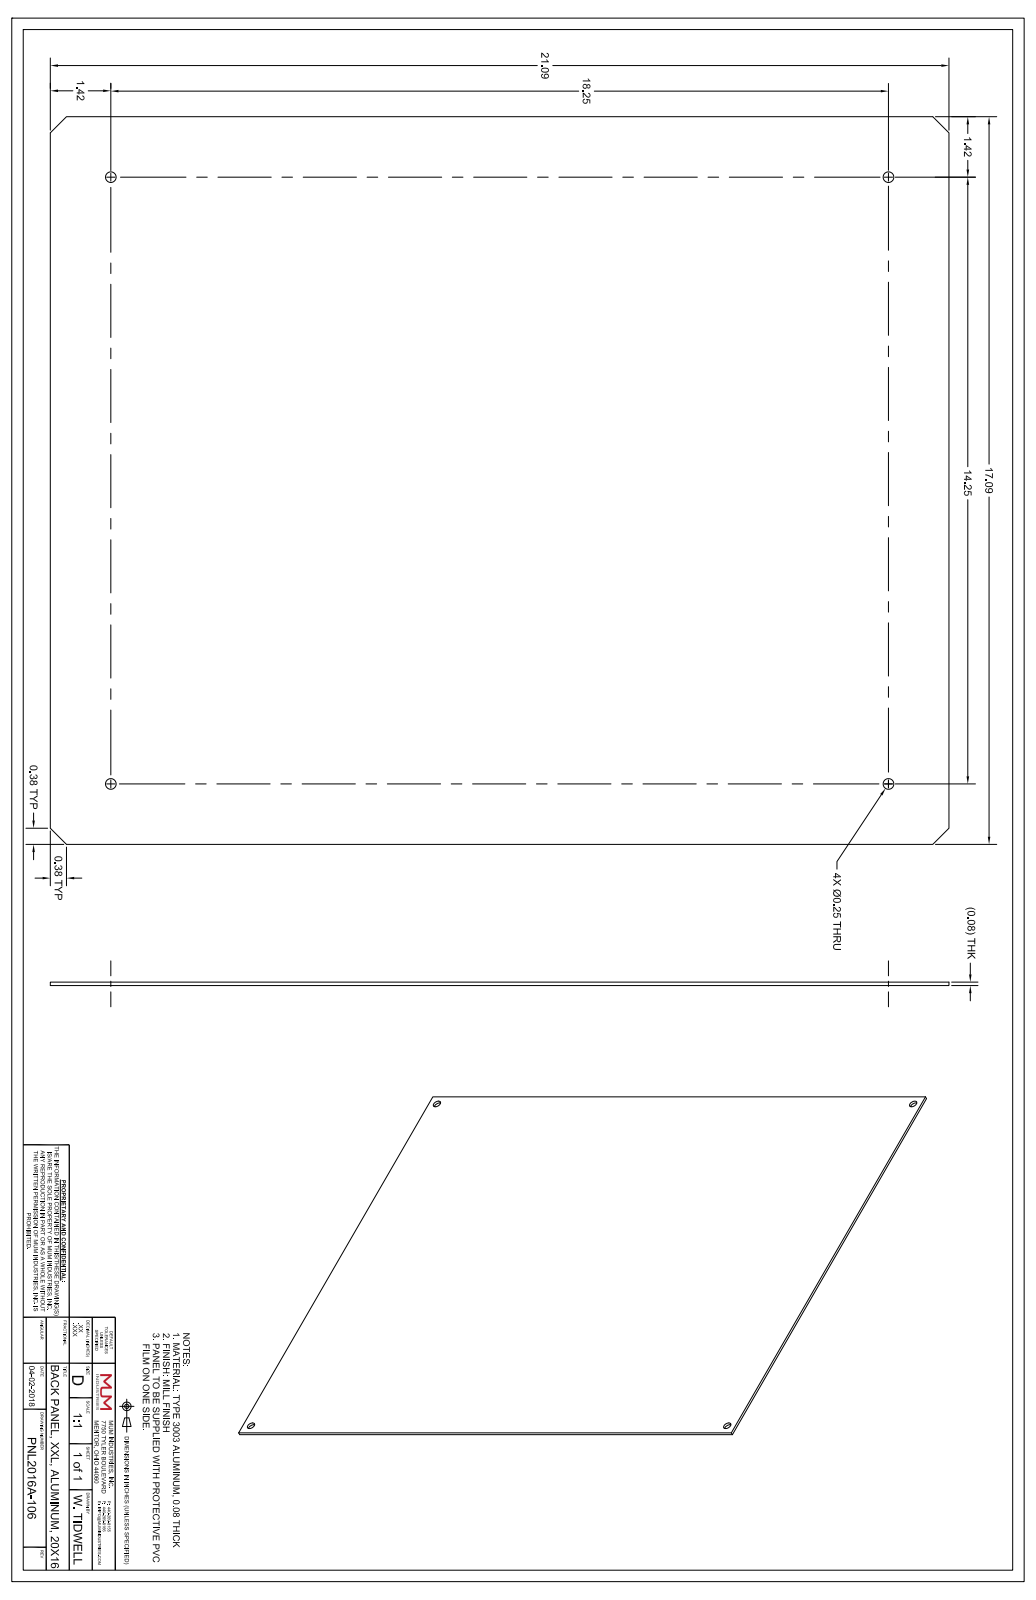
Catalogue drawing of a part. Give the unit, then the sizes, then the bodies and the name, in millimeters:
Units: millimetres
Overall size (bounding box): 535.7 × 434.1 × 2
Round holes (diameter × count): ⌀6.4 ×4
Main face-to-face distances: 2, 434.1, 535.7, 672.2
Hole centre spacings: 362, 463.6, 588.1
Volume: 471 900 mm³ · Surface area: 468 500 mm²
Bodies: 1 solid, 14 faces (10 planar, 4 cylindrical, 0 other)
Part name (STEP PRODUCT): ABP-2016-XXL-P10
STEP written by: SolidWorks 2018 (AUTOMOTIVE_DESIGN)
